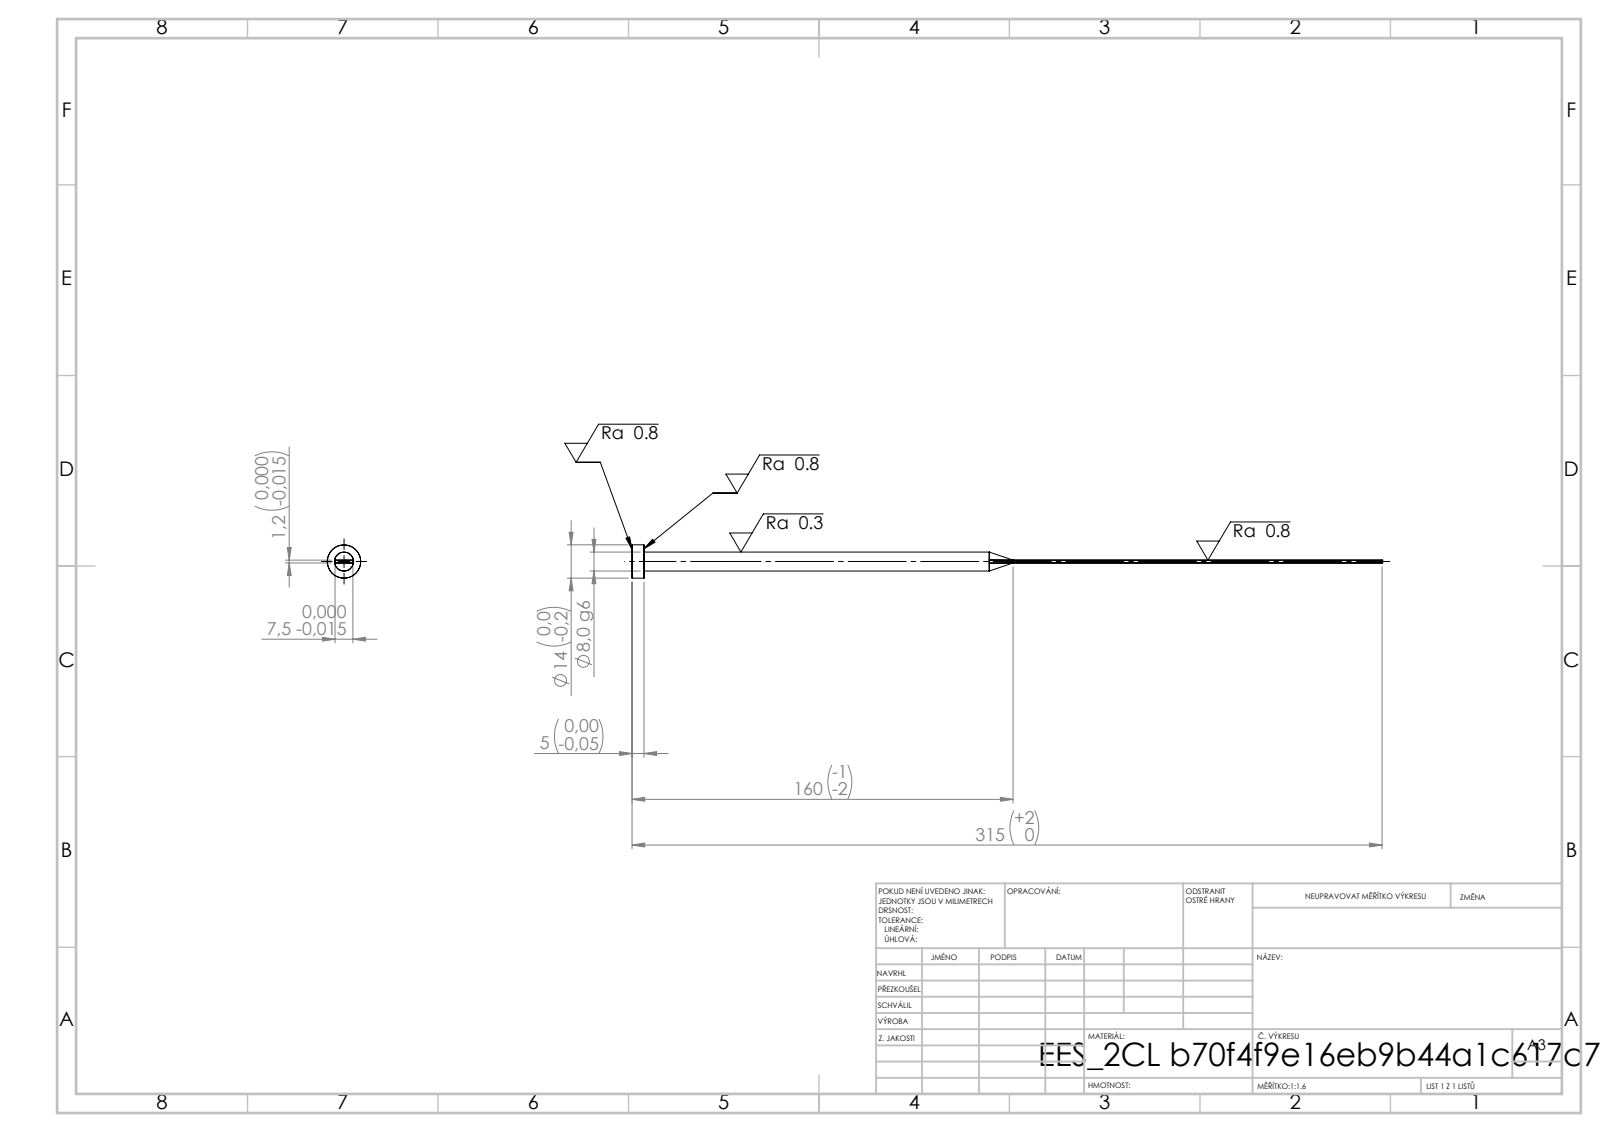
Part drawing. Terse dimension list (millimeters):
written by: SolidWorks 2019 (CONFIG_CONTROL_DESIGN)
unit: mm
bodies: 1 solid, 15 faces (7 planar, 4 cylindrical, 4 other)
size: 315 × 14 × 14
volume: 9 732 mm³; area: 7 035 mm²
bosses: 1× ⌀14, 1× ⌀8
face distances: 1.2, 7.5, 5, 315, 310
